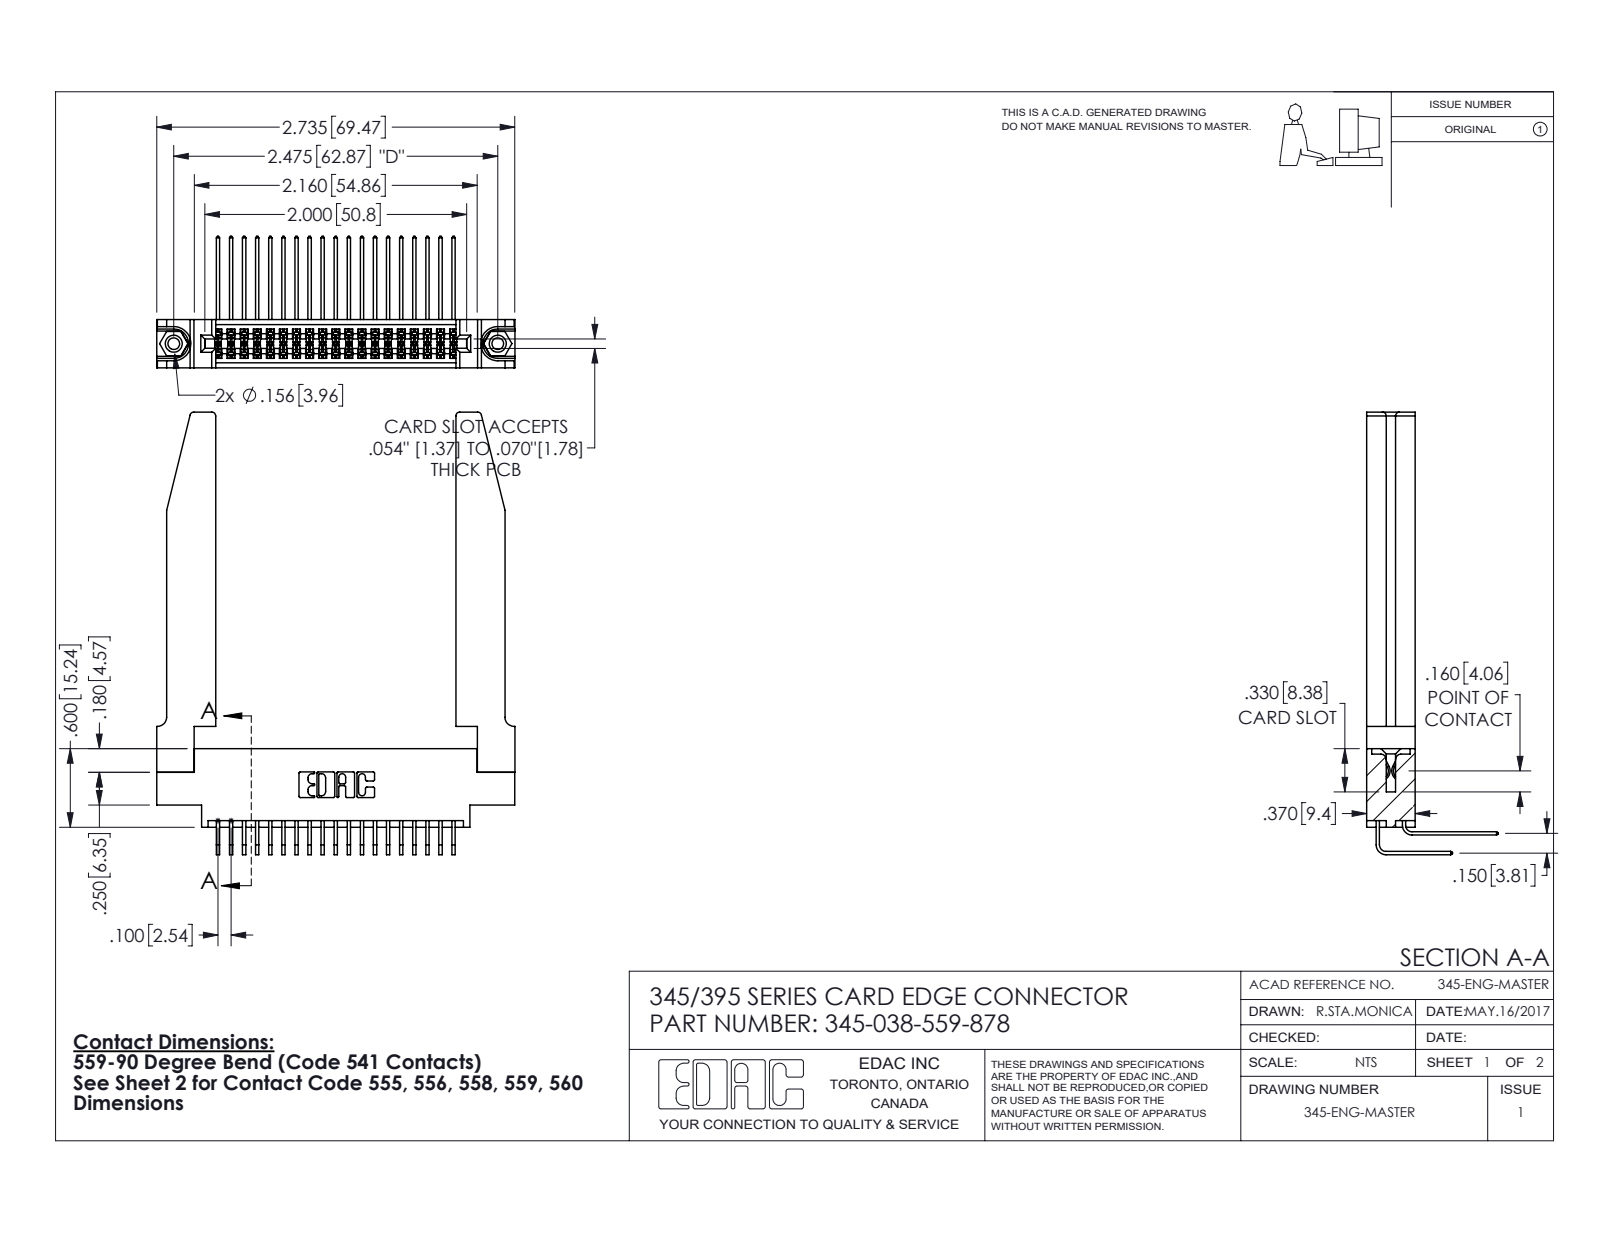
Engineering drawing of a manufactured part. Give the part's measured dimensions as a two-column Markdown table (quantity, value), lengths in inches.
| quantity | value |
| --- | --- |
| part name | 345-038-559-878; 345-292-001_558 559 Tail - 1; 345-220-078_345-220-078; 345-250-001_345-250-001-102 (+2 more) |
| STEP written by | SolidWorks 2016 (CONFIG_CONTROL_DESIGN) |
| units | inches |
| bodies | 43 solids, 2340 faces (1556 planar, 732 cylindrical, 52 other) |
| overall size | 3.379 × 2.736 × 1.005 |
| volume | 0.88 in³ |
| surface area | 26.95 in² |
| round holes (diameter × count) | 0.089 × 2, 0.125 × 2, 0.156 × 2, 0.064 × 1 |
| round bosses / shafts (diameter × count) | 0.155 × 2 |
| partial cylindrical surfaces (radius × count) | 0.006 × 75, 0.01 × 22, 0.03 × 8, 0.007 × 6, 0.031 × 6, 0.026 × 3, 0.014 × 2, 0.019 × 2 |
| main face-to-face distances | 0.37, 0.072, 0.298, 0.2, 0.098, 0.272, 0.025, 0.148, 0.15, 0.15 |
| hole center spacings | 0.27, 2.241, 2.475 |
